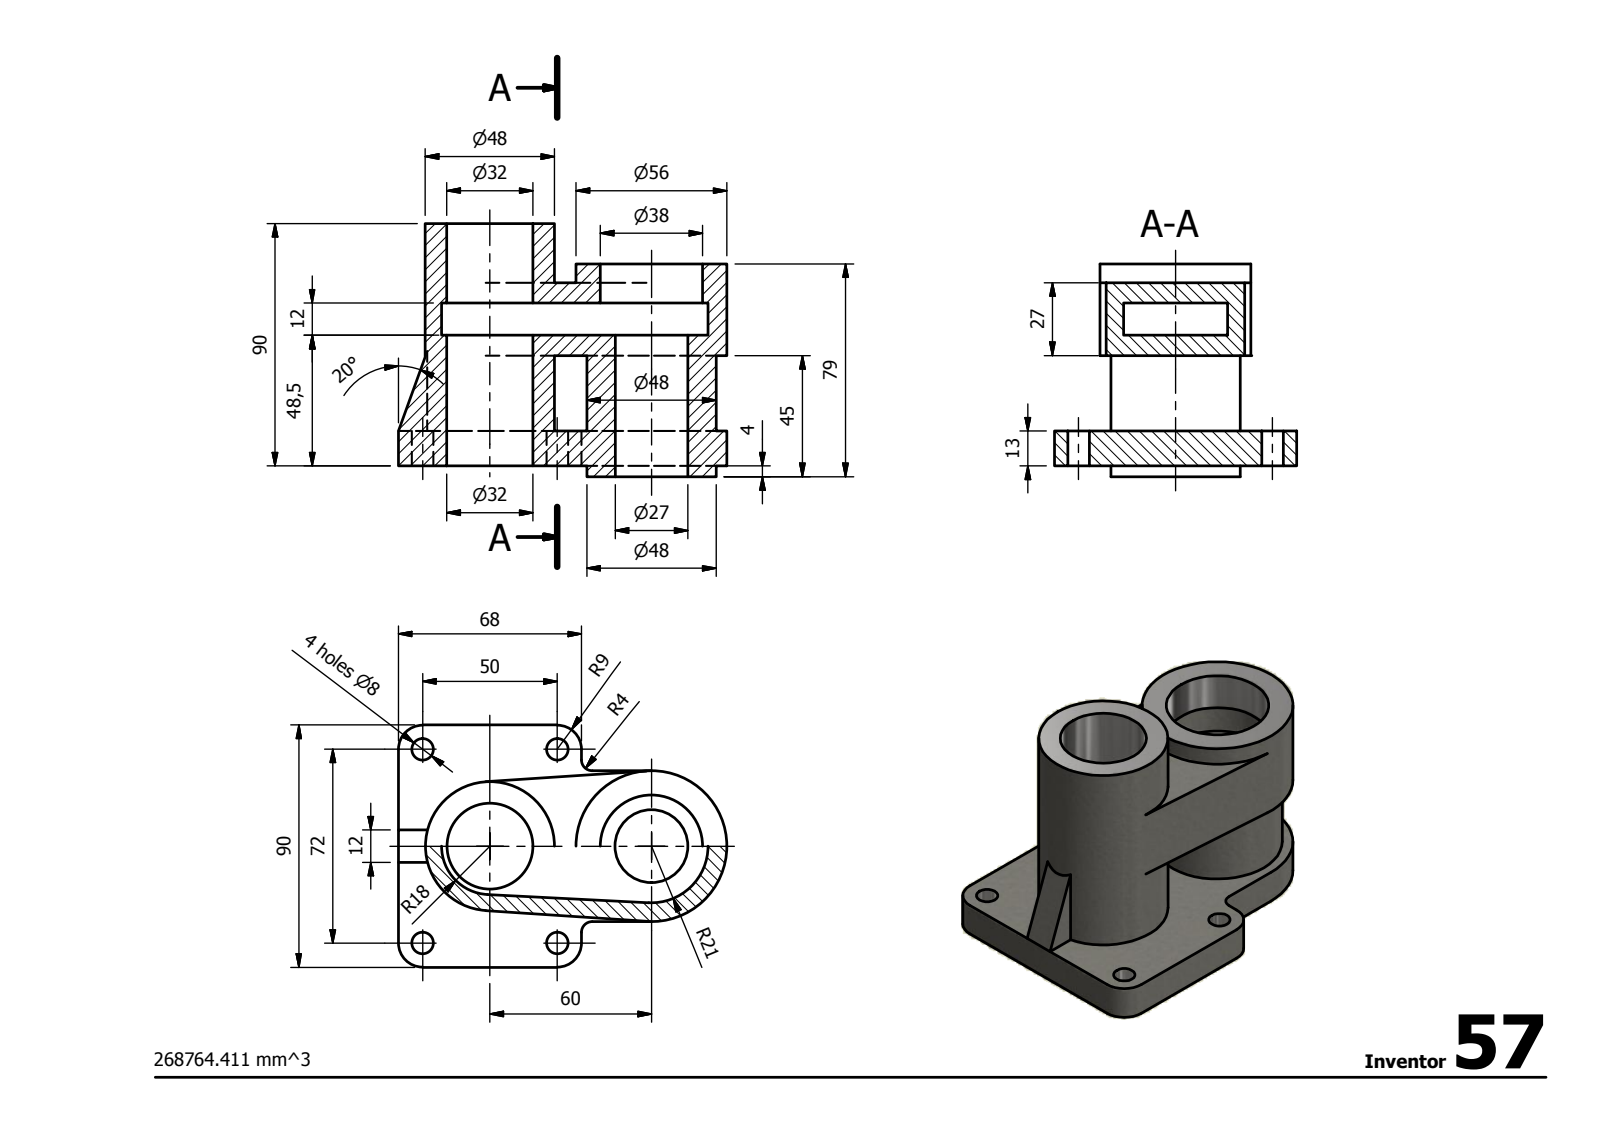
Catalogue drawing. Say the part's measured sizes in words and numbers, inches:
Its 3-D file was written by "Autodesk Inventor 2014 (AUTOMOTIVE_DESIGN)". It is 1 solid with 44 faces: 23 planar, 21 cylindrical and 0 other. Overall it measures 4.803 by 3.701 by 3.543 inches. Its volume is 16.4 cubic inches and its surface area 101.5 square inches. Round holes: 4 of diameter 0.315, 1 of diameter 1.063, 1 of diameter 1.26, 1 of diameter 1.496. Round bosses or shafts: 2 of diameter 1.89, 1 of diameter 2.205. Partial cylindrical surfaces (rounded edges, fillets, slot ends): 4 of radius 0.354, 2 of radius 0.157, 1 of radius 0.709, 1 of radius 0.827. The main face-to-face distances are 0.512, 0.295, 0.768, 1.909, 1.398, 0.669, 0.472, 3.543, 1.339, 1.614. The hole center spacings are 1.726, 1.969, 1.977, 2.835, 3.451, 3.634, 2.362.
